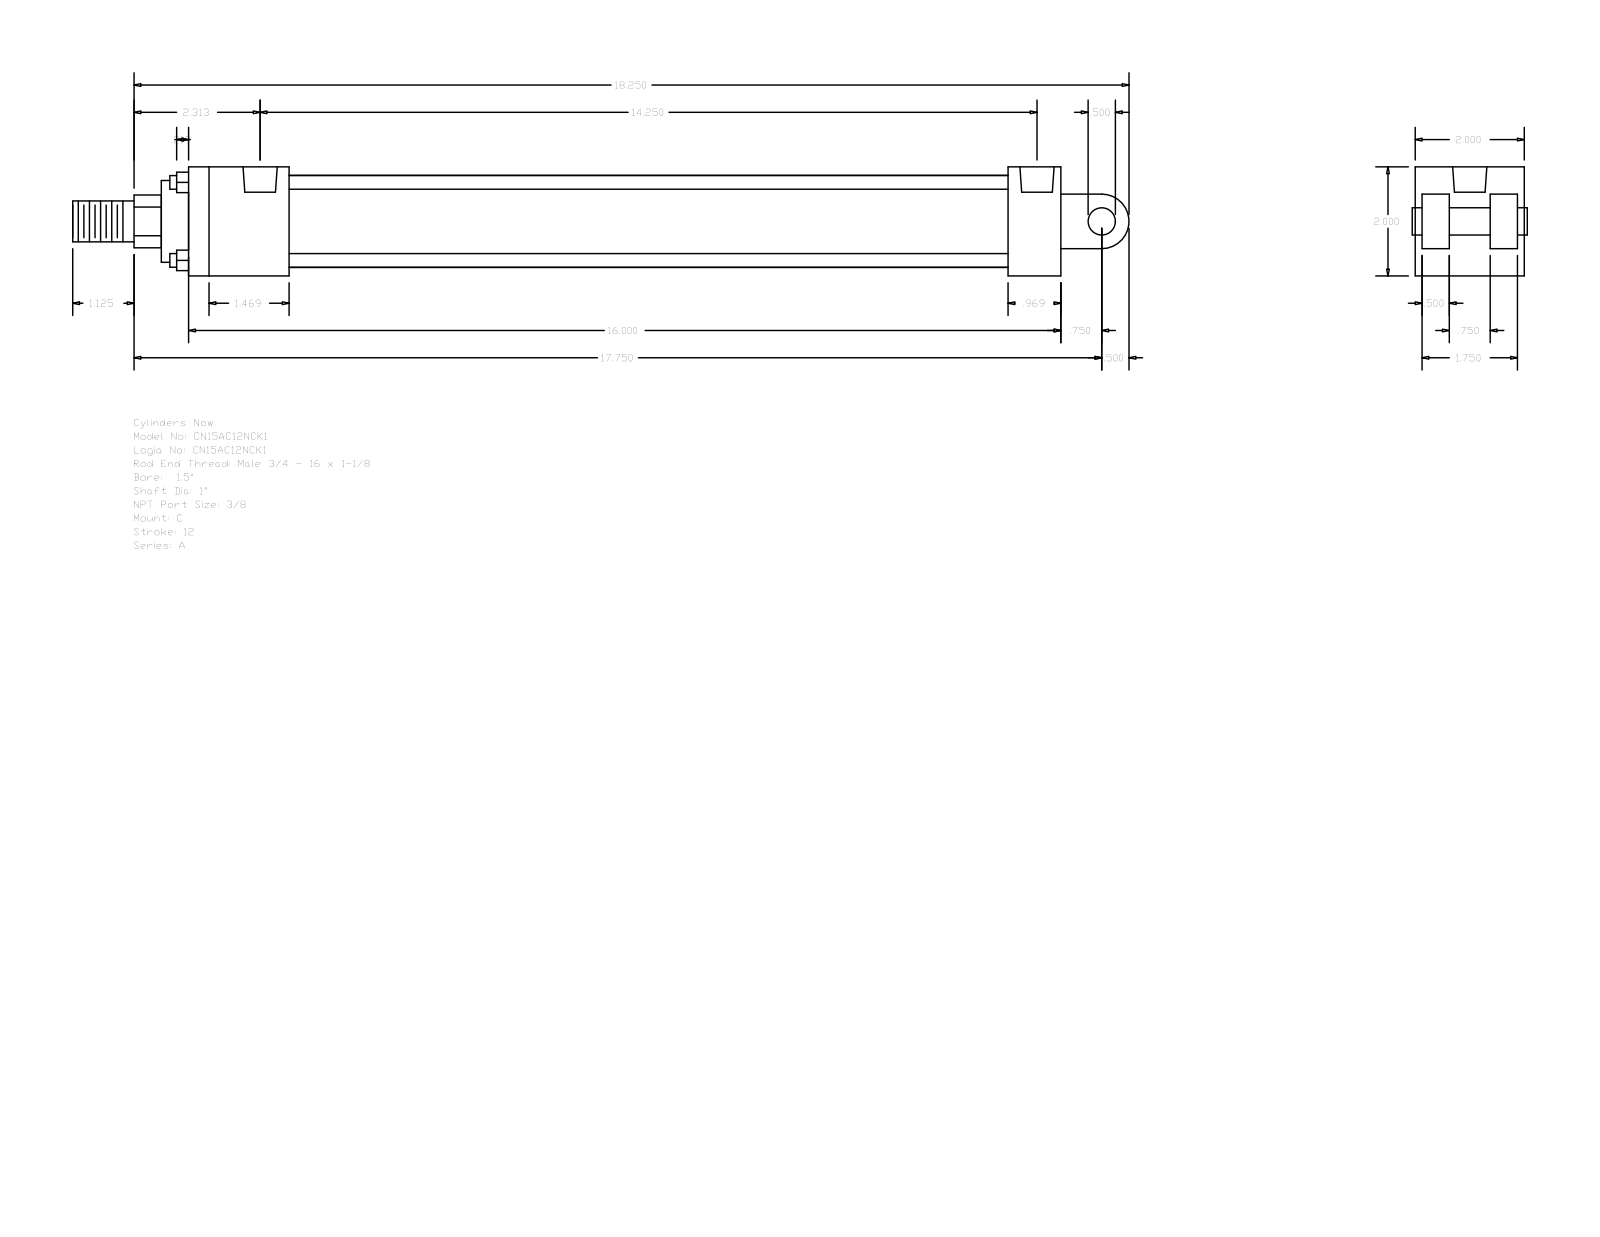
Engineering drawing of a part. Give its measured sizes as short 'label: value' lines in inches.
name: A_C__0150_1
written by: GSSL Pune (CONFIG_CONTROL_DESIGN)
unit: in
bodies: 0 solids, 99 faces (70 planar, 29 cylindrical, 0 other)
size: 19.375 × 2 × 2
holes: 4× ⌀0.219, 2× ⌀0.627
bosses: 4× ⌀0.25, 1× ⌀1.69, 1× ⌀1.5, 1× ⌀1, 1× ⌀0.75, 1× ⌀0.5
rounds: 1× R0.484, 1× R0.5
face distances: 2, 0.5, 0.125, 0.625, 1.375, 1.875, 1.25, 16, 1.5, 15.031
hole spacings: 0.156, 13.937, 14.094, 14.25
